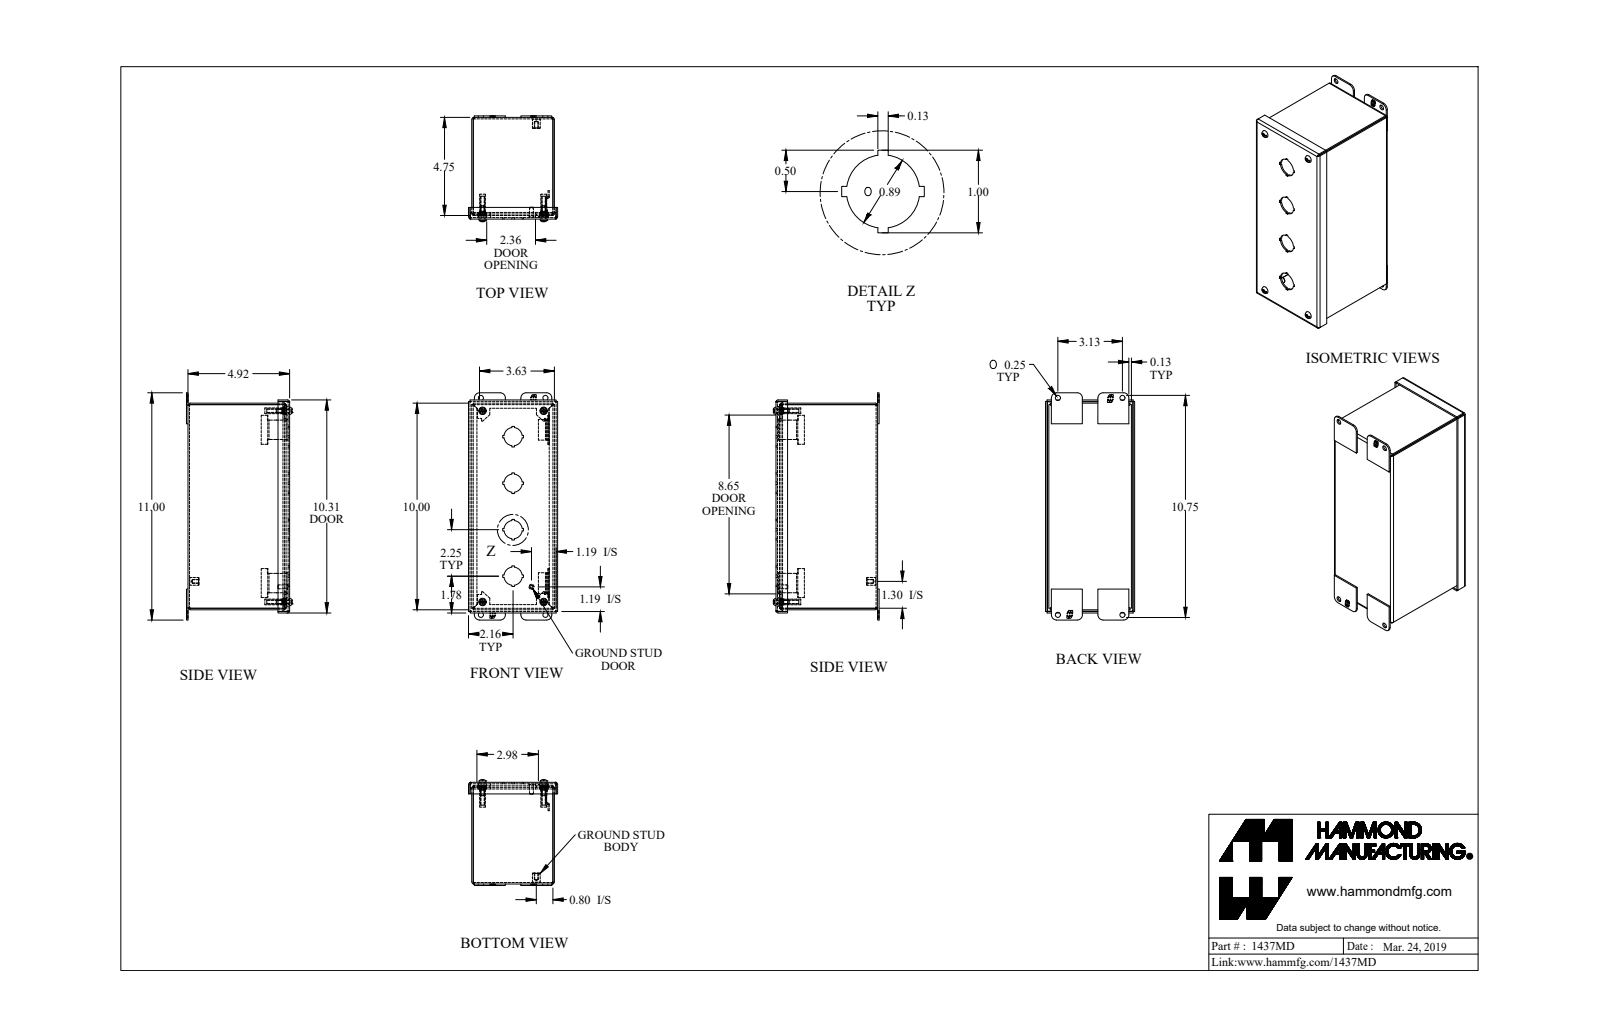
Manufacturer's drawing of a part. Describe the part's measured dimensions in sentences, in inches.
The part is named "1437MD_Default". Its 3-D file was written by "SolidWorks 2019 (CONFIG_CONTROL_DESIGN)". It is 23 solids with 779 faces: 547 planar, 176 cylindrical and 56 other. Overall it measures 11 by 5.121 by 4.312 inches. Its volume is 20.18 cubic inches and its surface area 537.9 square inches. Round holes: 8 of diameter 0.25, 4 of diameter 0.159, 4 of diameter 0.406, 4 of diameter 0.886, 1 of diameter 0.156. Round bosses or shafts: 4 of diameter 0.39, 4 of diameter 0.275, 4 of diameter 0.19, 4 of diameter 0.148, 1 of diameter 0.375, 1 of diameter 0.25, 1 of diameter 0.188. Partial cylindrical surfaces (rounded edges, fillets, slot ends): 12 of radius 0.036, 12 of radius 0.108, 8 of radius 0.25, 4 of radius 0.029, 4 of radius 0.086, 4 of radius 0.16, 4 of radius 0.171, 2 of radius 0.125. The main face-to-face distances are 0.072, 3.928, 4.85, 4.922, 4, 3.856, 4.778, 9.928, 0.156, 4.084. The hole center spacings are 9.25, 9.875, 10.333, 3.106, 0.631, 1.937, 2.961, 3.107.
